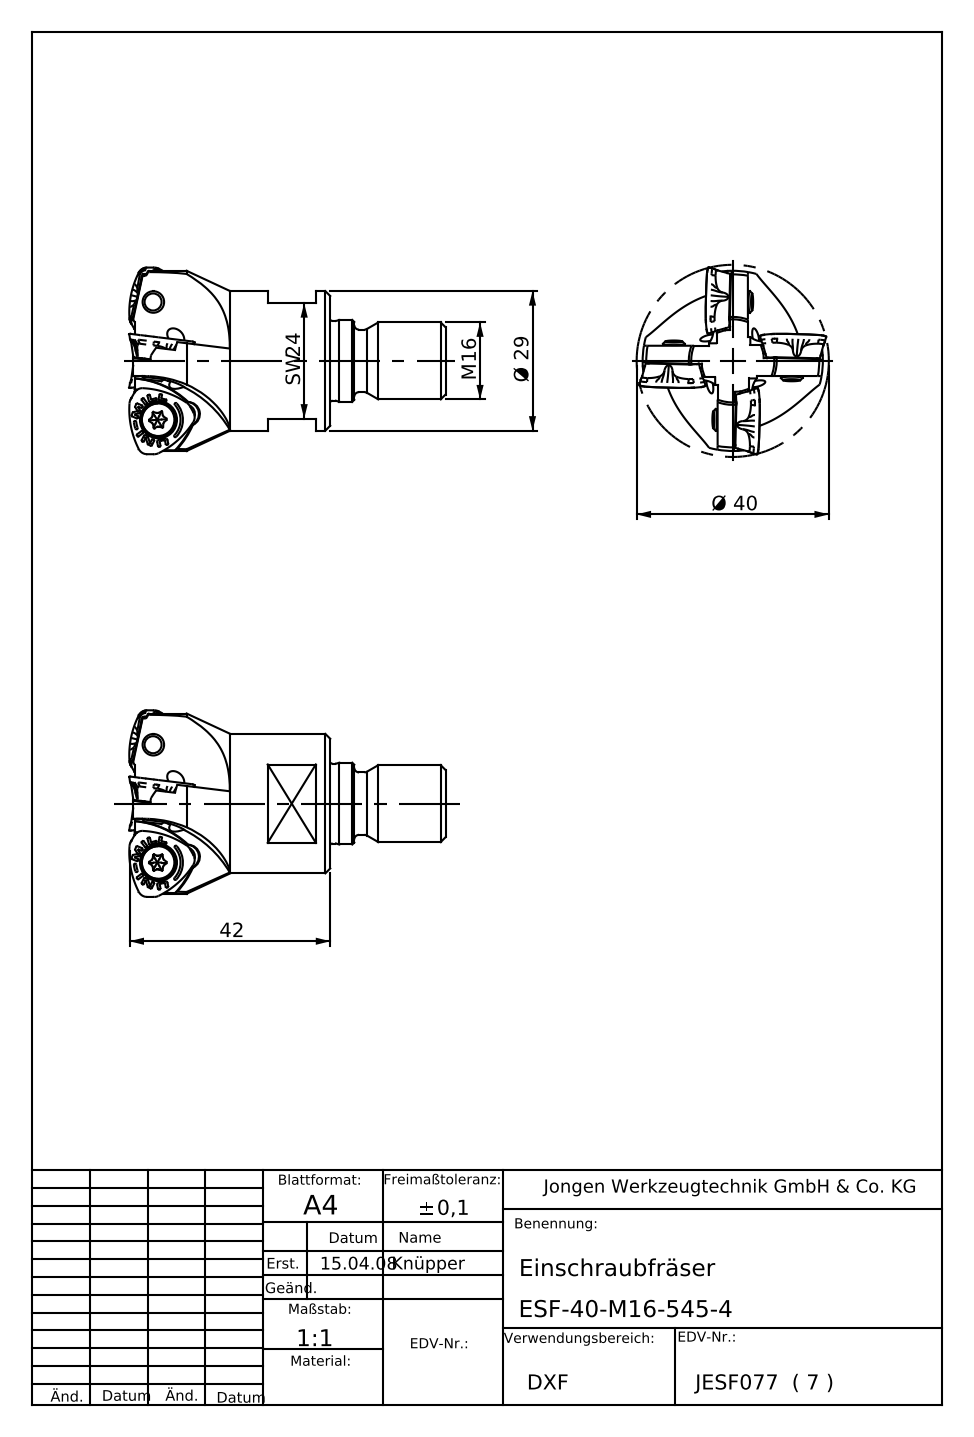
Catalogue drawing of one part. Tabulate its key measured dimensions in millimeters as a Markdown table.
| quantity | value |
| --- | --- |
| part name | ESF-40-M16-545-4 |
| STEP written by | SolidWorks 2013 (AUTOMOTIVE_DESIGN) |
| units | millimeters |
| bodies | 1 solid, 126 faces (54 planar, 50 cylindrical, 22 other) |
| overall size | 66.02 × 39.93 × 39.93 |
| volume | 35 461 mm³ |
| surface area | 9 077 mm² |
| round holes (diameter × count) | 3 × 4, 4 × 1 |
| round bosses / shafts (diameter × count) | 29 × 1, 17 × 1, 16.6 × 1, 16 × 1, 13 × 1 |
| partial cylindrical surfaces (radius × count) | 18 × 8, 1.5 × 4, 2.5 × 4, 22.85 × 4, 18.75 × 1 |
| main face-to-face distances | 24, 64.7, 40.7, 27, 37, 3, 13, 10, 37.7, 27.7 |
